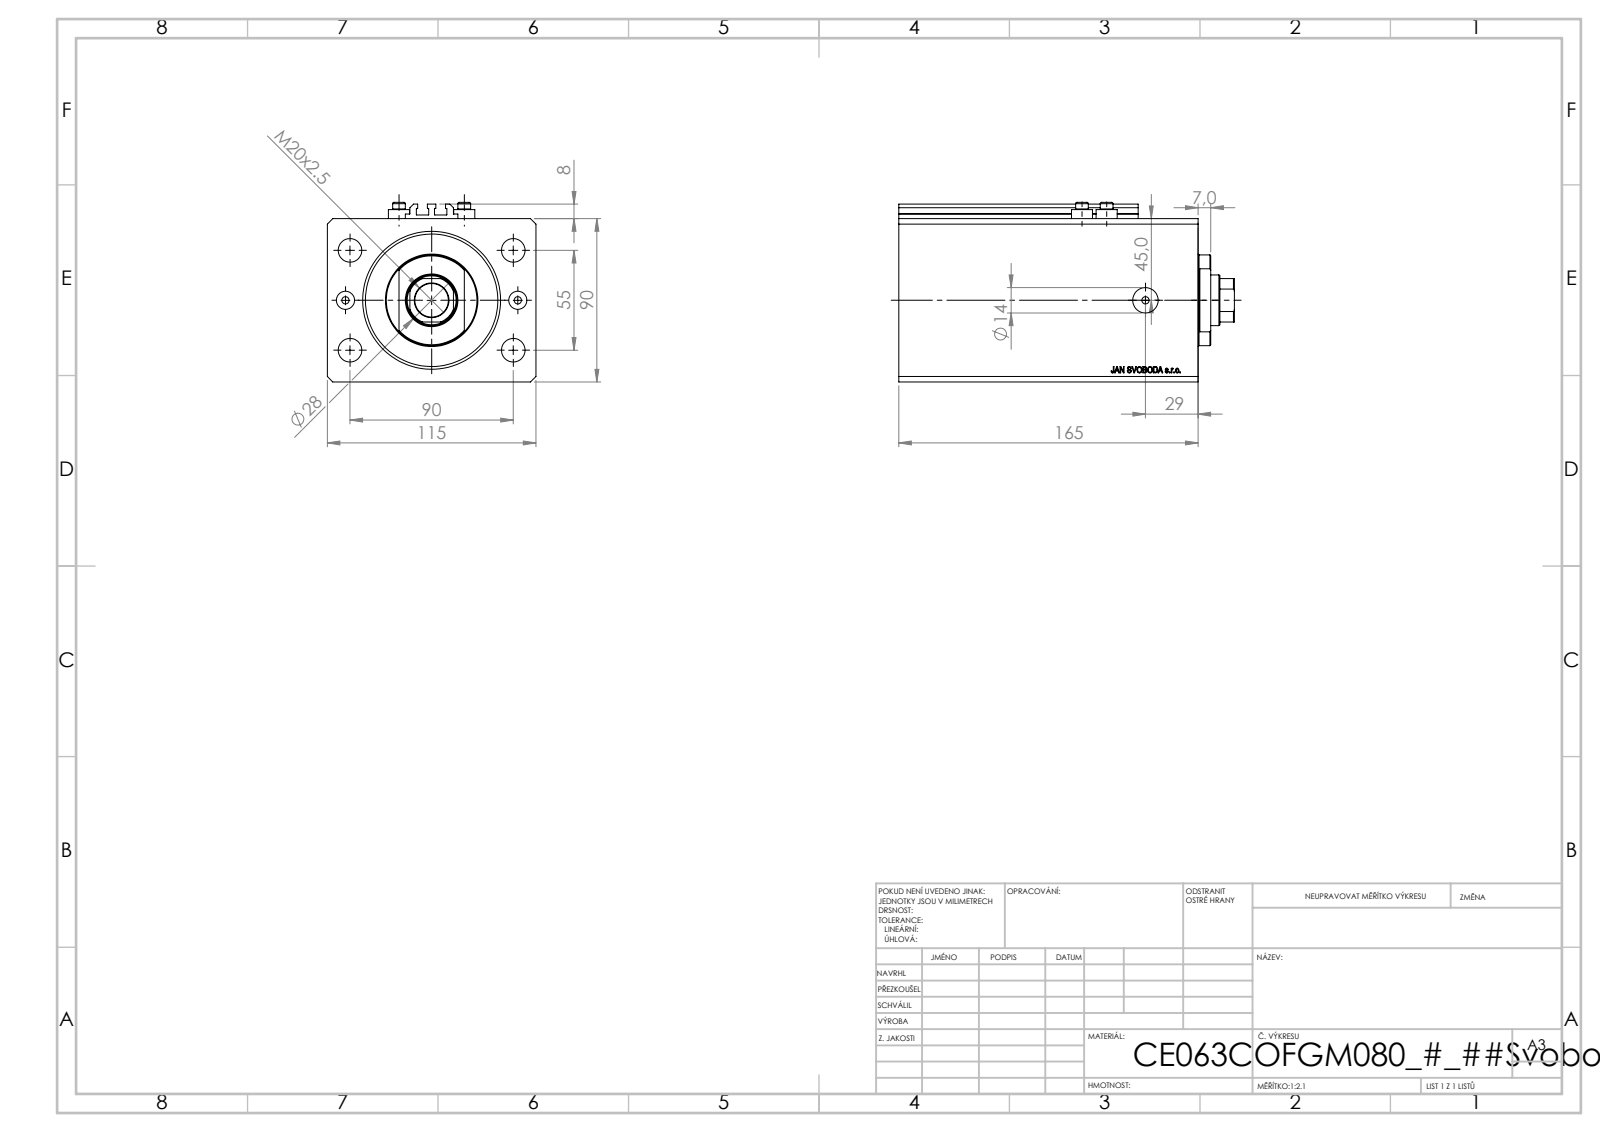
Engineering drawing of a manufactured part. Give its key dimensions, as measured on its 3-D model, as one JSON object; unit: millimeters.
{"part_name": "V250CE_VC_C; V250CE_C_Body; ALLEN BOLT V250CE; V250CE_C_VCP", "step_written_by": "SolidWorks 2019 (CONFIG_CONTROL_DESIGN)", "units": "millimeters", "bodies": {"solids": 8, "faces": 1034, "planar": 504, "cylindrical": 86, "other": 444}, "overall_size": [185, 115, 99], "volume_mm3": 1442000, "surface_area_mm2": 204842, "round_holes": [[4, 8], [13, 4], [10, 2], [14, 2], [18.5, 1], [28, 1], [63, 1], [76, 1]], "round_bosses_or_shafts": [[11.6, 4], [7, 4], [50, 1]], "partial_cylinders_radius": [[0.2, 10], [13.5, 1]], "face_to_face_distances": [90, 115, 165, 17.9, 147.1, 20, 145, 127.1, 65, 80], "hole_center_spacings": [27.61, 52.74, 96.5, 13.6, 36, 38.48, 47.5, 55]}
